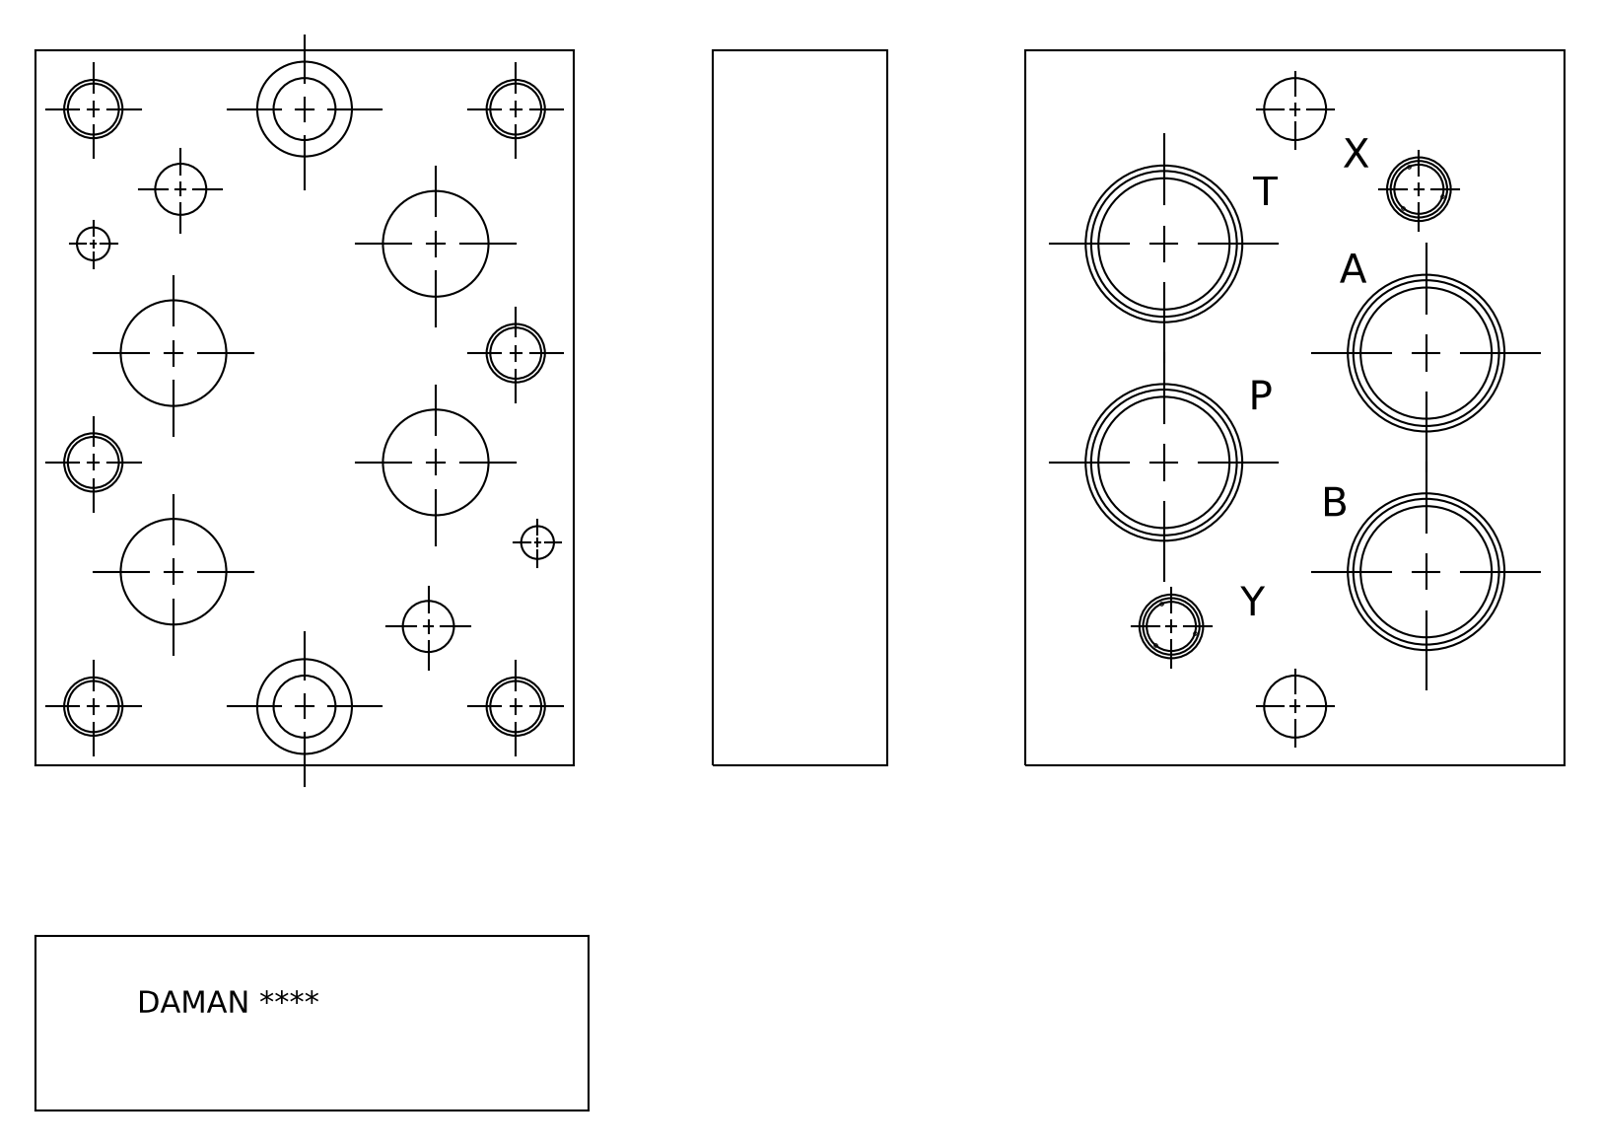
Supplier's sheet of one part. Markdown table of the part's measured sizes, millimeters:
| quantity | value |
| --- | --- |
| part name | Part_AD08SPB16P_3D |
| STEP written by | Autodesk Inventor 2020 (AUTOMOTIVE_DESIGN) |
| units | millimeters |
| bodies | 1 solid, 491 faces (310 planar, 34 cylindrical, 147 other) |
| overall size | 155.57 × 117.47 × 38.1 |
| volume | 544 697 mm³ |
| surface area | 81 415 mm² |
| round holes (diameter × count) | 10.72 × 8, 12.7 × 6, 28.57 × 4, 33.71 × 4, 7.14 × 2, 13.49 × 2, 13.87 × 2, 20.62 × 2, 23.01 × 2, 23.02 × 2 |
| main face-to-face distances | 38.1, 117.47, 155.57, 19.1, 19, 19.05, 7.82, 11.18, 7.87, 26.92 |
| hole center spacings | 29.53, 46.07, 47.62, 53.18, 55.97, 61.92, 75.09, 76.99 |
